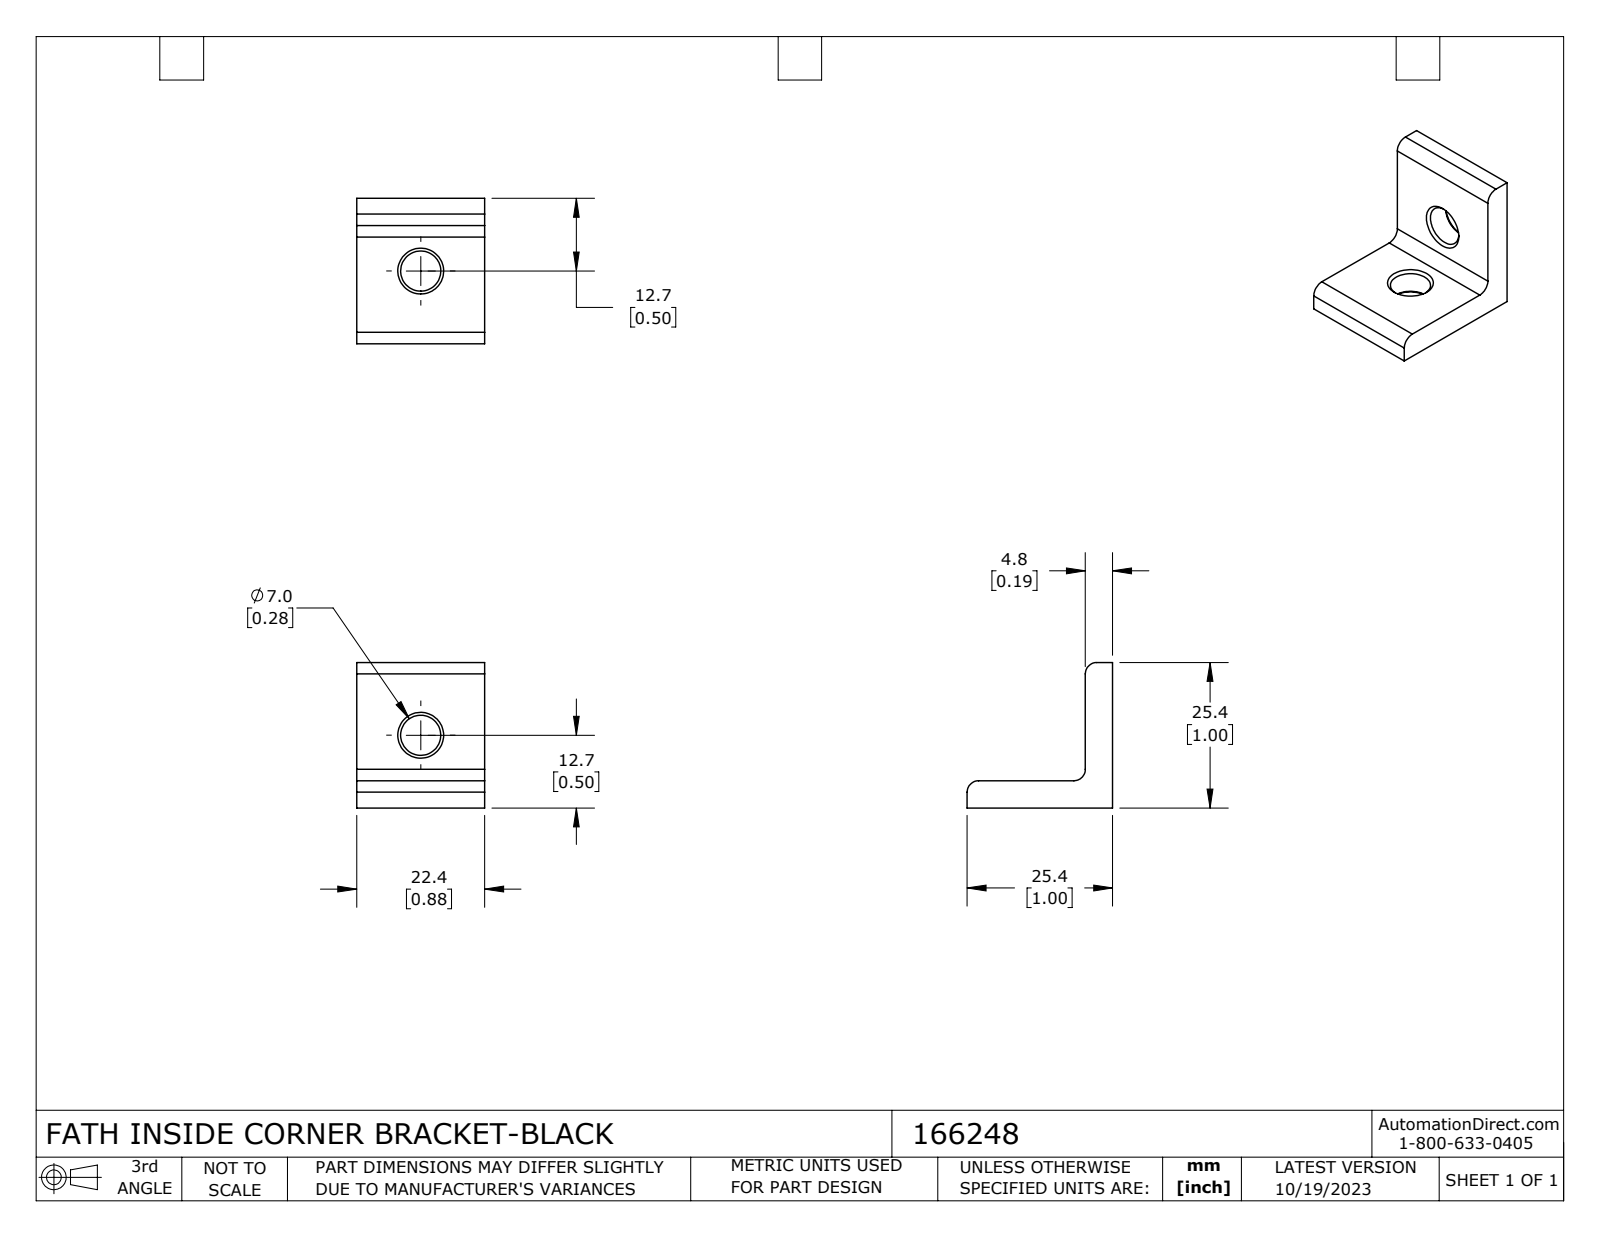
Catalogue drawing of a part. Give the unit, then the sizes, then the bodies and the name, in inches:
Units: inches
Overall size (bounding box): 1 × 1 × 0.88
Round holes (diameter × count): ⌀0.276 ×2
Partial cylindrical surfaces — rounded edges, fillets, slot ends (radius × count): R0.079 ×3
Main face-to-face distances: 0.187, 0.88, 1, 0.813
Volume: 0.275 in³ · Surface area: 4.156 in²
Bodies: 1 solid, 23 faces (8 planar, 7 cylindrical, 8 other)
Part name (STEP PRODUCT): 166248
STEP written by: SolidWorks 2023 (CONFIG_CONTROL_DESIGN)
